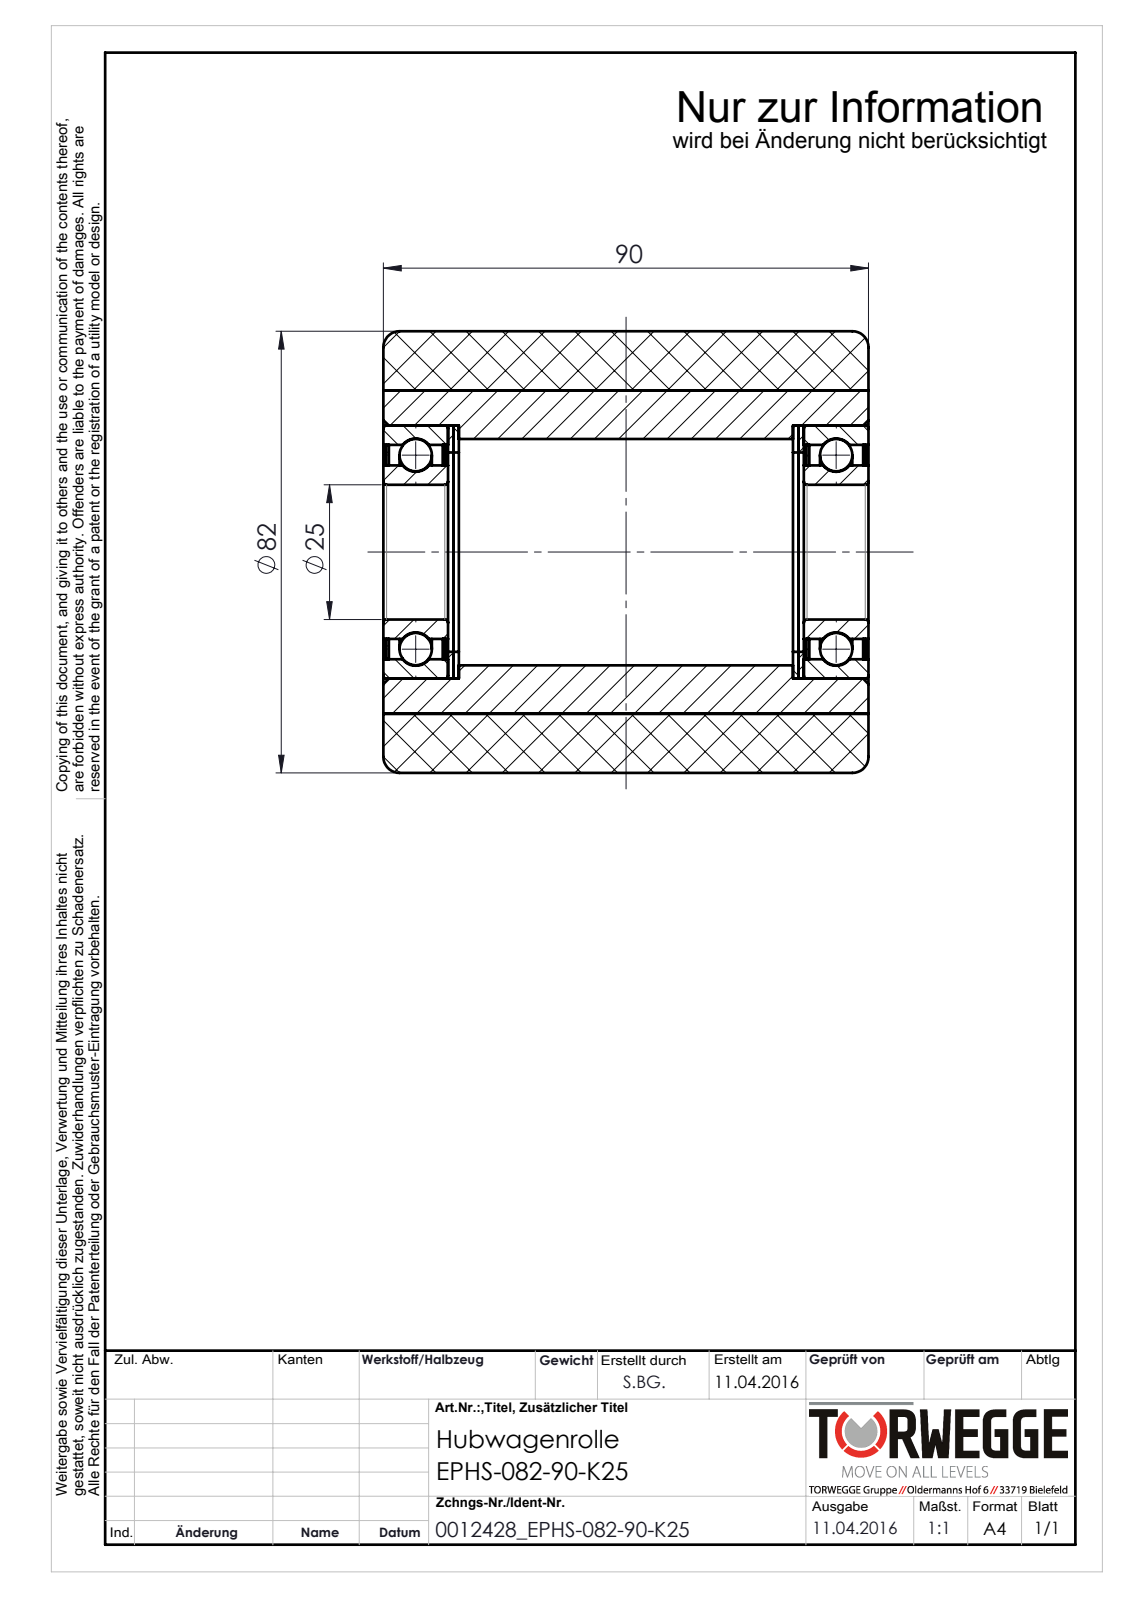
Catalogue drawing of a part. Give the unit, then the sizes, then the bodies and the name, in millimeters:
Units: millimetres
Overall size (bounding box): 90 × 82 × 82
Round holes (diameter × count): ⌀25 ×1, ⌀32.2 ×1, ⌀37 ×1, ⌀39.8 ×1, ⌀42 ×1, ⌀60 ×1
Round bosses / shafts (diameter × count): ⌀82 ×1, ⌀47 ×1
Main face-to-face distances: 1, 78, 12, 0.5, 13, 77, 65, 90, 64, 76
Volume: 367 175 mm³ · Surface area: 104 948 mm²
Bodies: 16 solids, 158 faces (30 planar, 68 cylindrical, 60 other)
Part name (STEP PRODUCT): 0012428_EPHS-082-90-K25
STEP written by: SolidWorks 2016 (AUTOMOTIVE_DESIGN)
